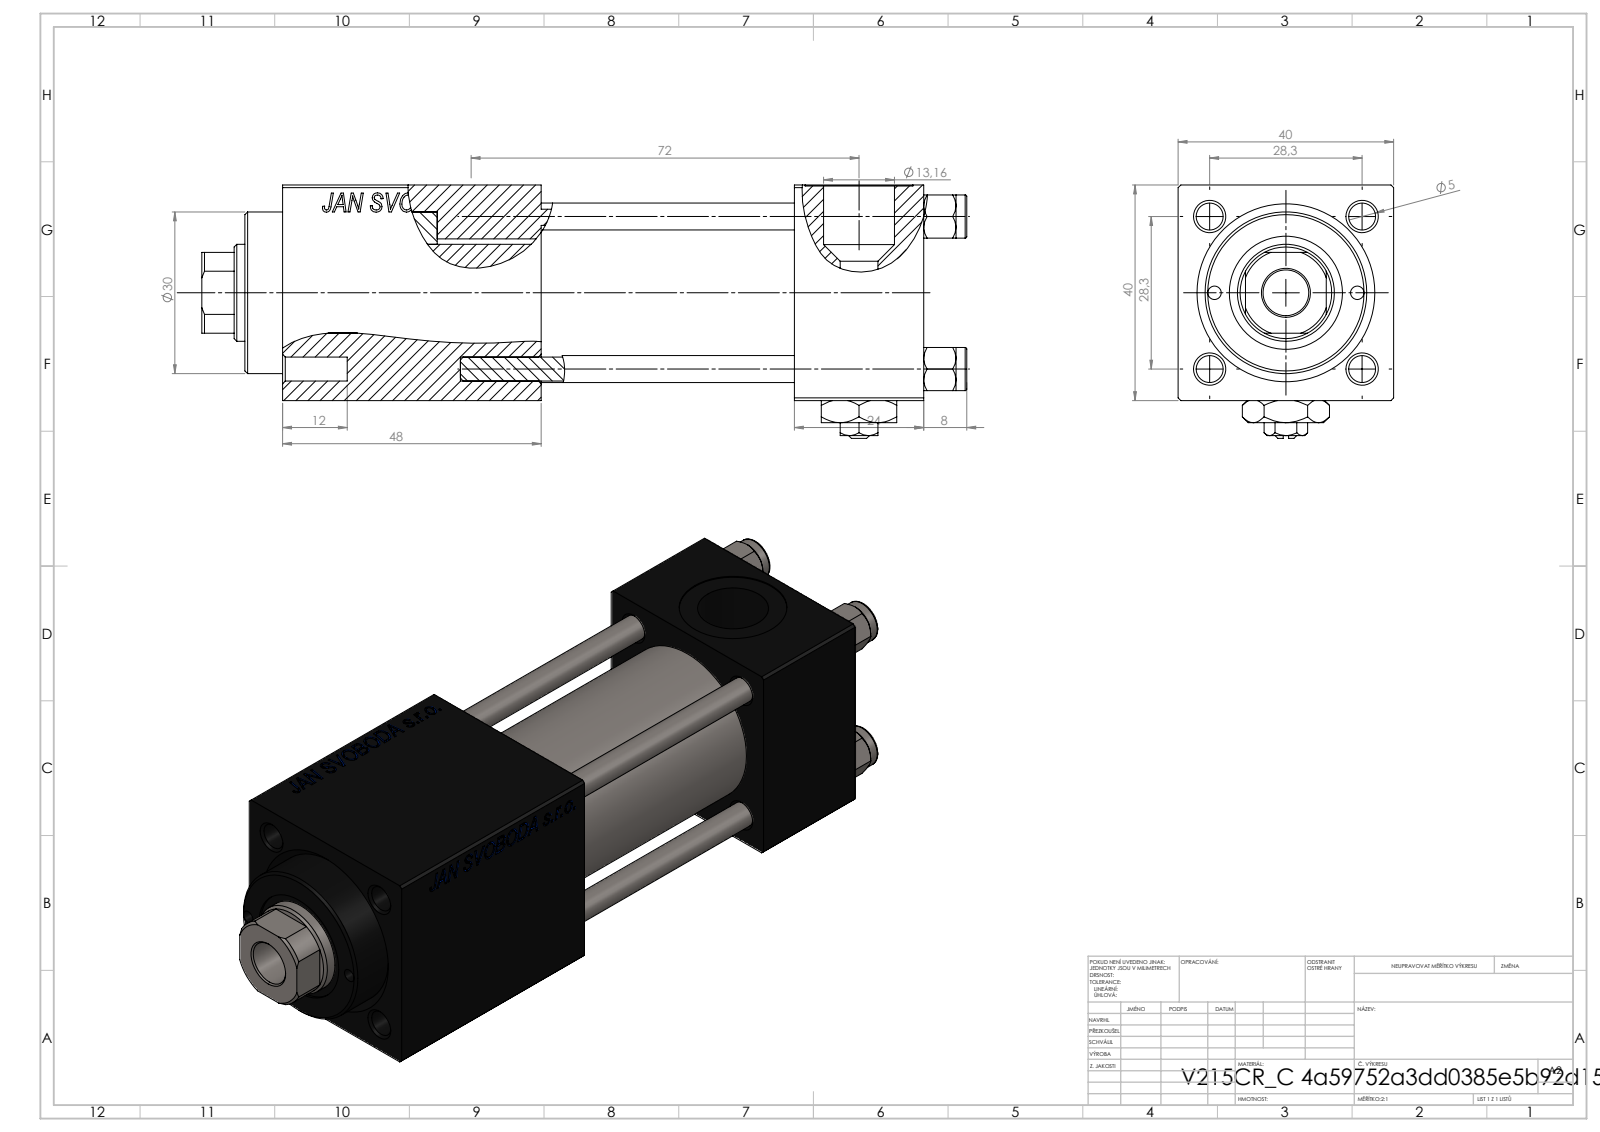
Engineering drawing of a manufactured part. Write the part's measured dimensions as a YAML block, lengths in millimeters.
part_name: "NUT_M5_C; V215CR_C_TYCINKA; V215_VC_A; V215CR_VCP_C (+2 more)"
step_written_by: "SolidWorks 2019 (CONFIG_CONTROL_DESIGN)"
units: millimeters
bodies: {solids: 12, faces: 1203, planar: 549, cylindrical: 96, other: 558}
overall_size: [142, 47, 40]
volume: 148723
surface_area: 57995
round_holes:
  - {diameter: 5, count: 4}
  - {diameter: 20, count: 3}
  - {diameter: 2.5, count: 2}
  - {diameter: 7, count: 2}
  - {diameter: 13.16, count: 2}
  - {diameter: 8.5, count: 1}
  - {diameter: 18, count: 1}
  - {diameter: 21, count: 1}
  - {diameter: 25, count: 1}
  - {diameter: 30, count: 1}
round_bosses_or_shafts:
  - {diameter: 8, count: 4}
  - {diameter: 31, count: 1}
partial_cylinders:
  - {radius: 8.5, count: 1}
face_to_face_distances: [40, 24, 71, 47, 90.3, 66.3, 19.3, 48, 39.8, 95]
hole_center_spacings: [14.18, 20.01, 28.3, 30.84, 13.25, 40.02, 26.5, 72]
